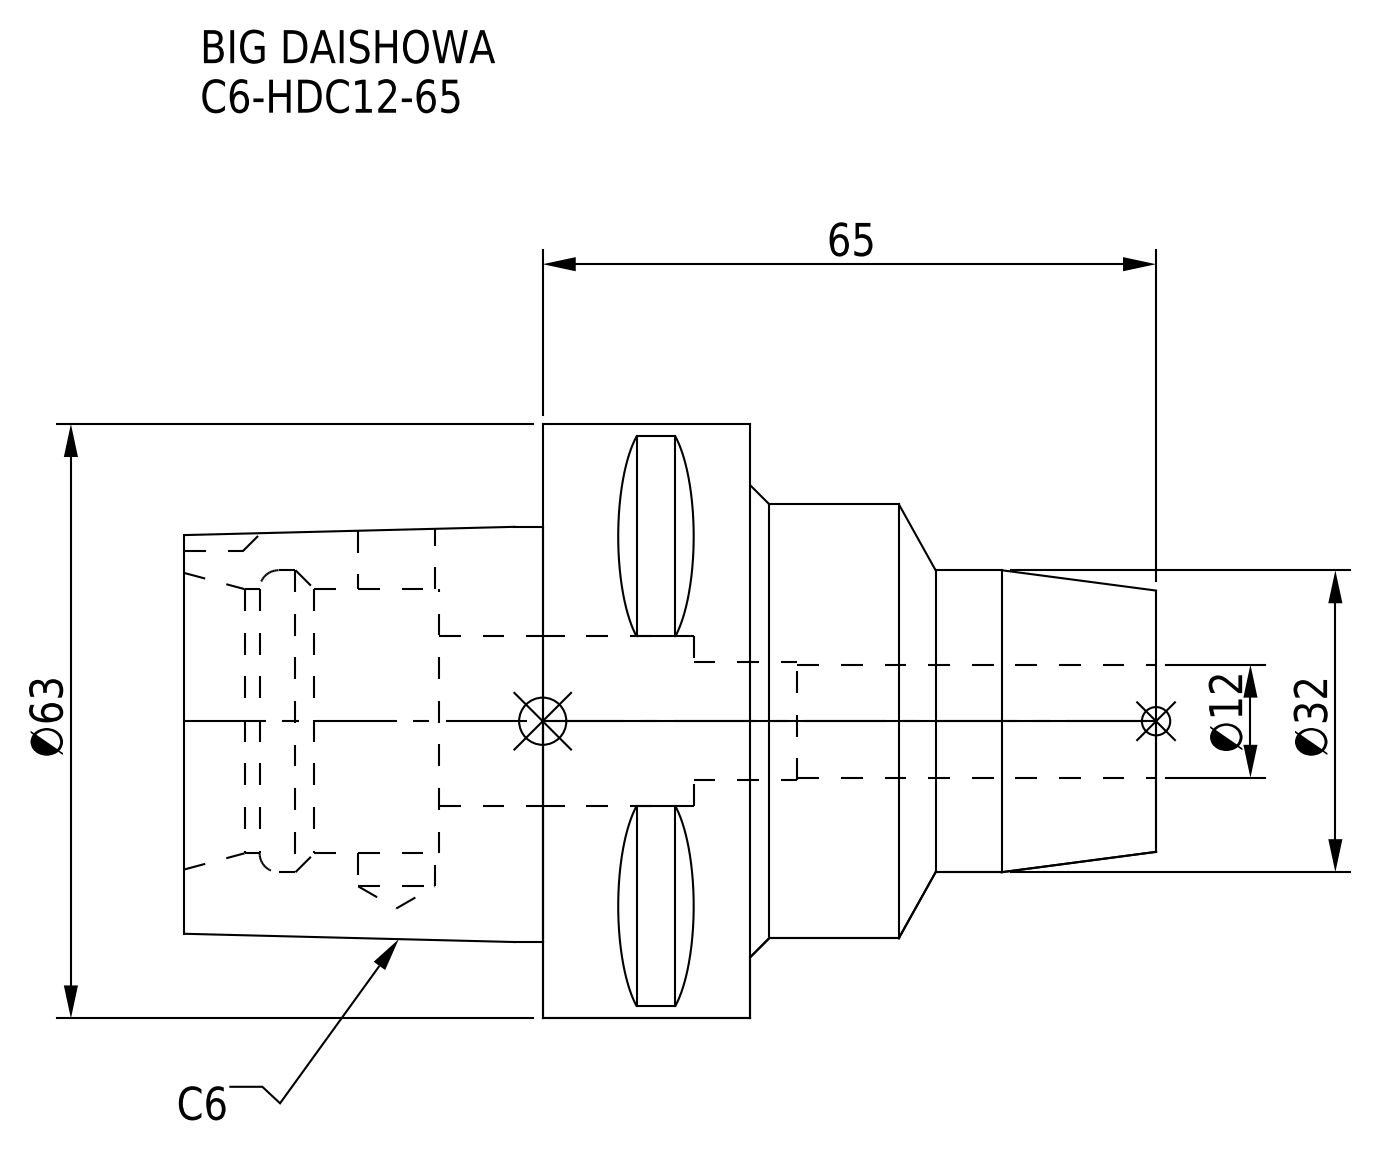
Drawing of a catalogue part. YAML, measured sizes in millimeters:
part_name: "C6-HDC12-65"
step_written_by: "CREO PARAMETRIC BY PTC INC, 2016380 (AUTOMOTIVE_DESIGN)"
units: millimeters
bodies: {solids: 1, faces: 68, planar: 29, cylindrical: 23, other: 16}
overall_size: [103, 63, 63]
volume: 139191
surface_area: 26071
round_holes:
  - {diameter: 8.1, count: 1}
  - {diameter: 12, count: 1}
  - {diameter: 12.5, count: 1}
  - {diameter: 18, count: 1}
  - {diameter: 28, count: 1}
  - {diameter: 32, count: 1}
round_bosses_or_shafts:
  - {diameter: 63, count: 1}
  - {diameter: 46, count: 1}
partial_cylinders:
  - {radius: 5, count: 1}
face_to_face_distances: [22, 38, 27, 65, 60, 43, 103, 11, 76, 33]
